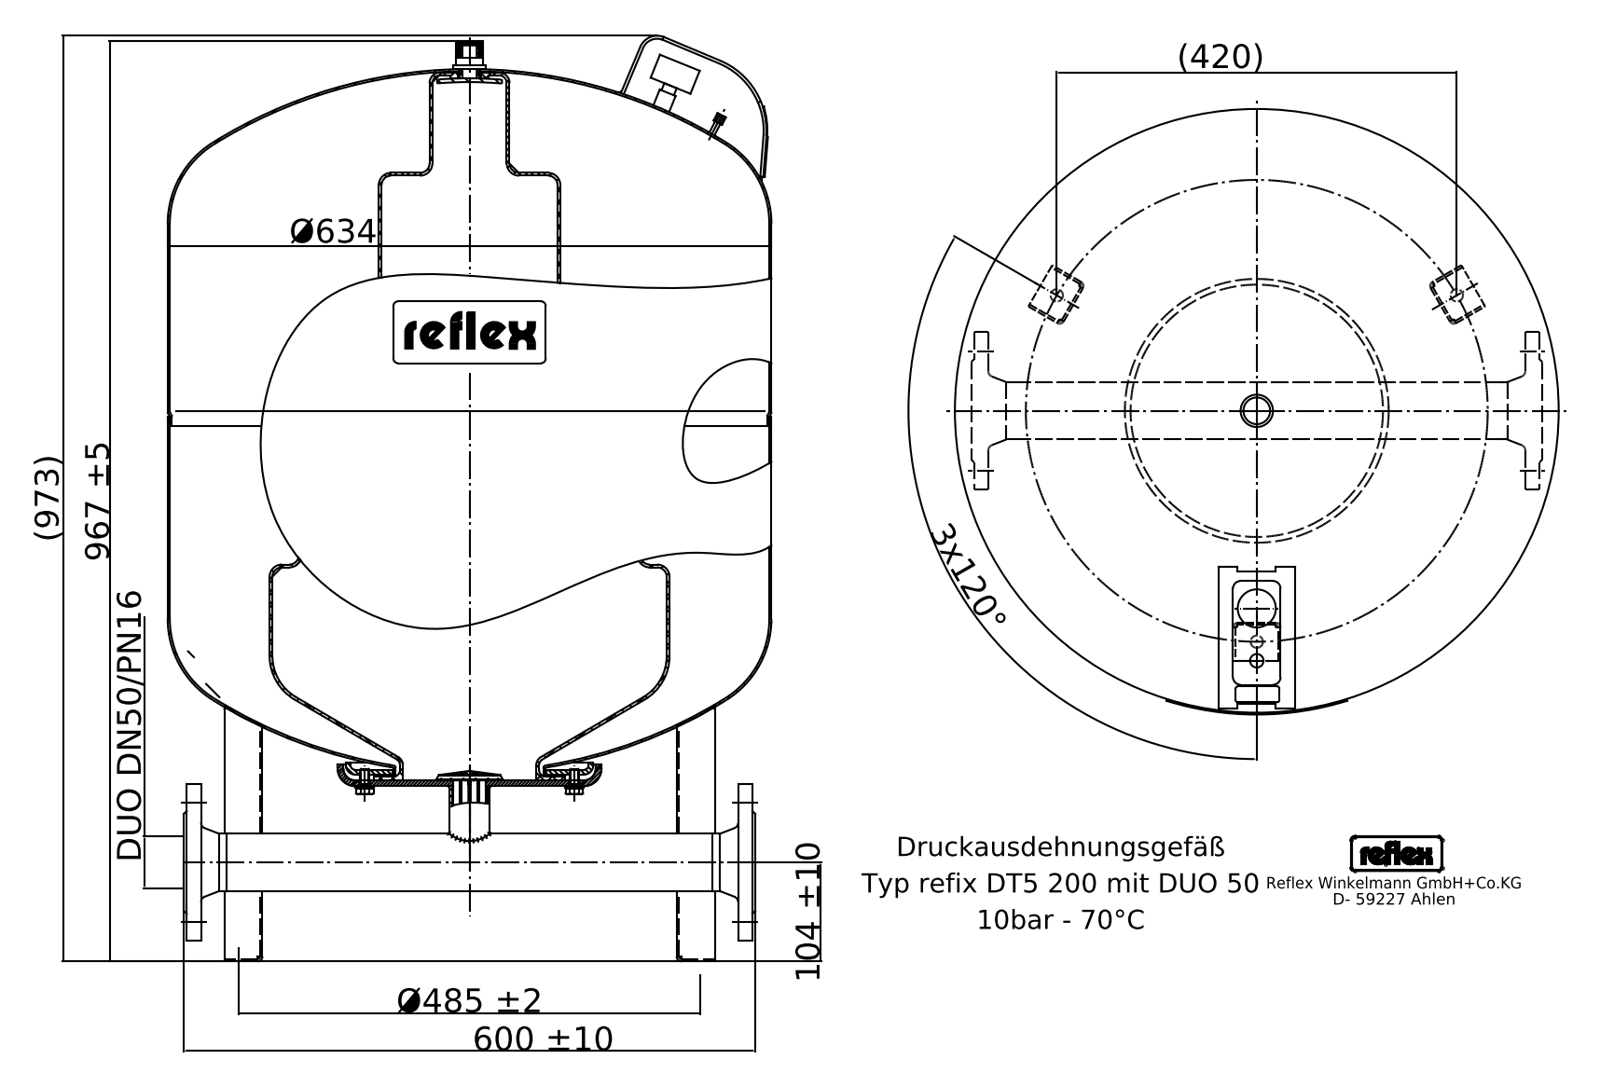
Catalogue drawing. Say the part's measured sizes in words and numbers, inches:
Its 3-D file was written by "Mechanical Desktop 2008 (CONFIG_CONTROL_DESIGN)". It is 23 solids with 521 faces: 223 planar, 185 cylindrical and 113 other. Overall it measures 38.126 by 24.961 by 24.961 inches. Its volume is 12 310 cubic inches and its surface area 5 723 square inches. Round holes: 4 of diameter 0.748, 3 of diameter 0.528, 1 of diameter 0.098, 1 of diameter 0.15, 1 of diameter 0.169, 1 of diameter 0.173, 1 of diameter 0.215, 1 of diameter 0.276, 1 of diameter 0.315, 1 of diameter 0.449, 1 of diameter 2.374, 1 of diameter 6.181. Round bosses or shafts: 9 of diameter 0.394, 1 of diameter 24.961, 1 of diameter 10.236, 1 of diameter 9.055, 1 of diameter 6.496, 1 of diameter 2.441, 1 of diameter 1.669, 1 of diameter 1.339. Partial cylindrical surfaces (rounded edges, fillets, slot ends): 15 of radius 0.039, 15 of radius 0.098, 15 of radius 0.197, 4 of radius 0.221, 3 of radius 0.089, 2 of radius 0.151, 2 of radius 0.266, 2 of radius 0.315. The main face-to-face distances are 16.378, 0.098, 1.87, 6.654, 23.031, 0.236, 6.89, 23.268, 1.969, 1.772. The hole center spacings are 2.46, 3.48, 9.547, 16.536, 4.921.
